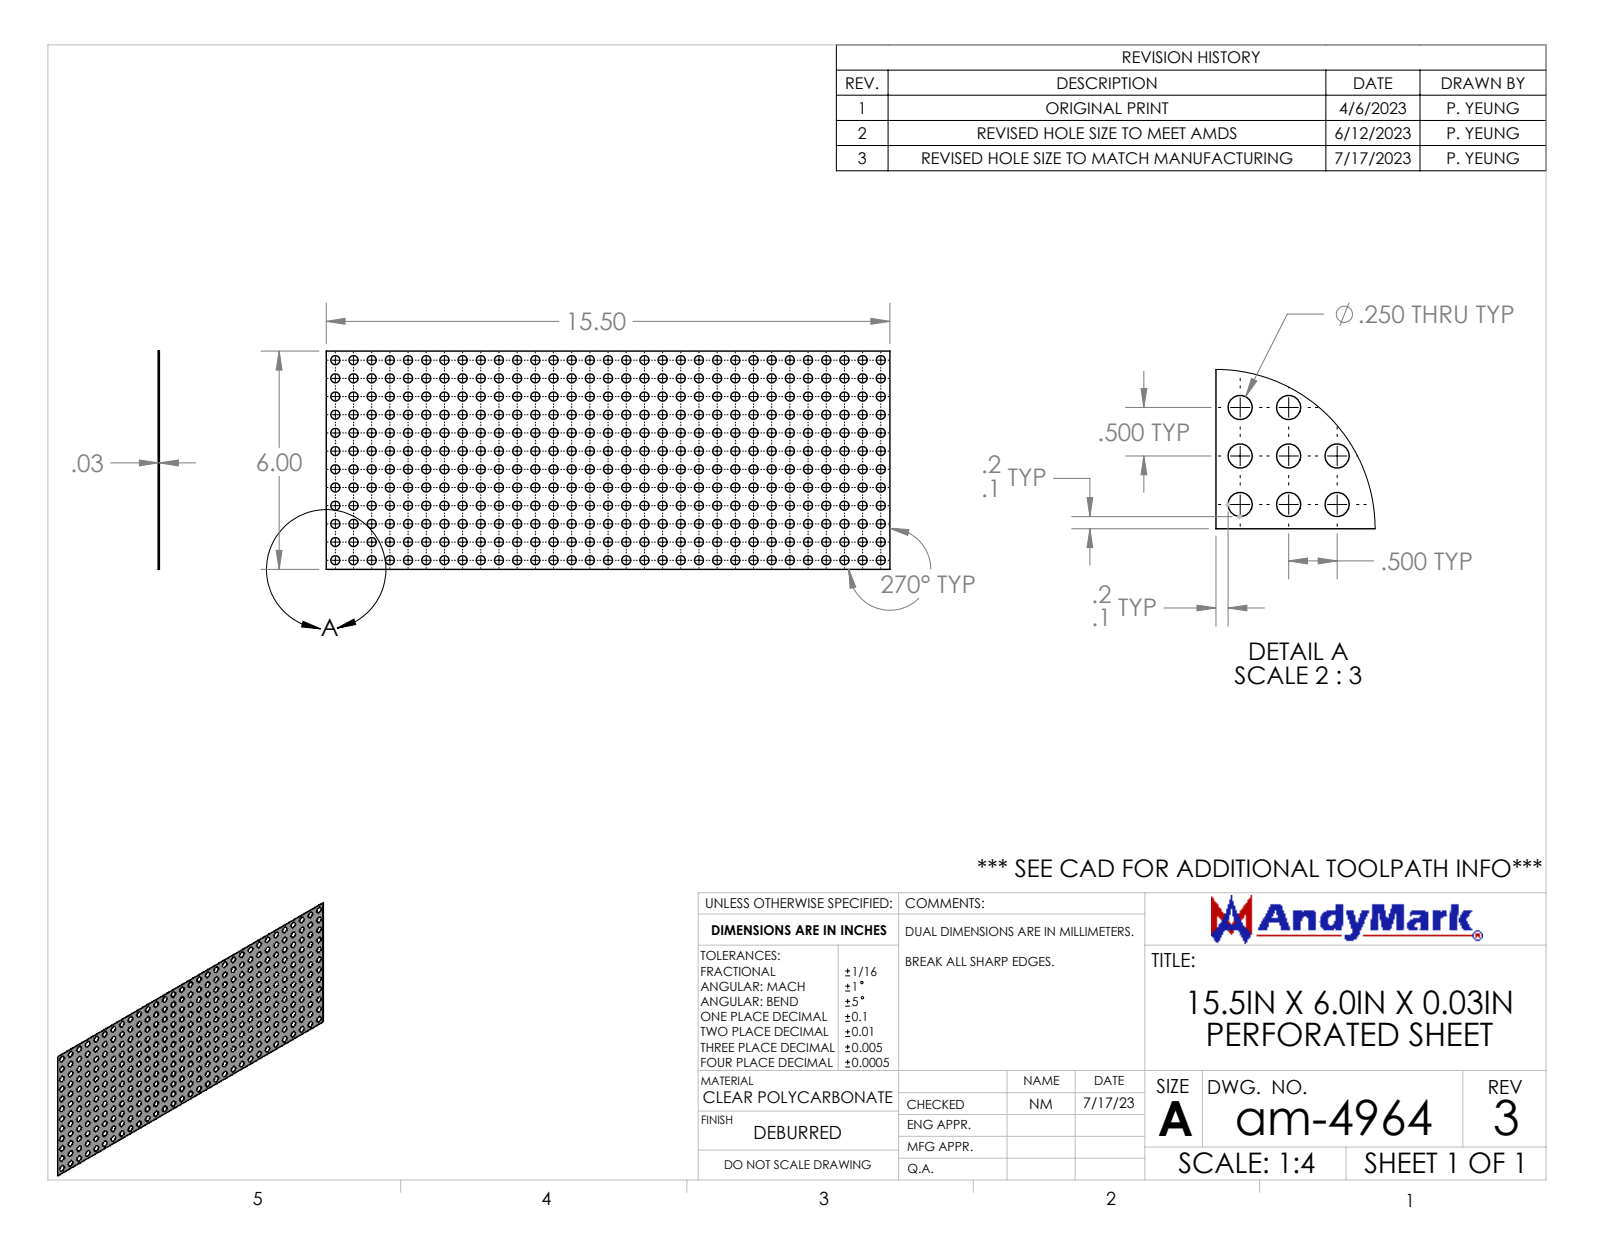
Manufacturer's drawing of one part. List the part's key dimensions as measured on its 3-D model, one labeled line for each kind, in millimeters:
Part name (STEP PRODUCT): am-4964 15.5IN x 6.0IN x 0.03IN Perforated Sheet
STEP written by: SolidWorks 2022 (CONFIG_CONTROL_DESIGN)
Units: millimetres
Bodies: 1 solid, 750 faces (6 planar, 744 cylindrical, 0 other)
Overall size (bounding box): 393.7 × 152.4 × 0.8
Volume: 38 280 mm³ · Surface area: 103 200 mm²
Round holes (diameter × count): ⌀6.4 ×372
Main face-to-face distances: 0.8, 152.4, 393.7
Hole centre spacings: 12.7, 25.4, 38.1, 50.8, 63.5, 76.2, 88.9, 101.6
